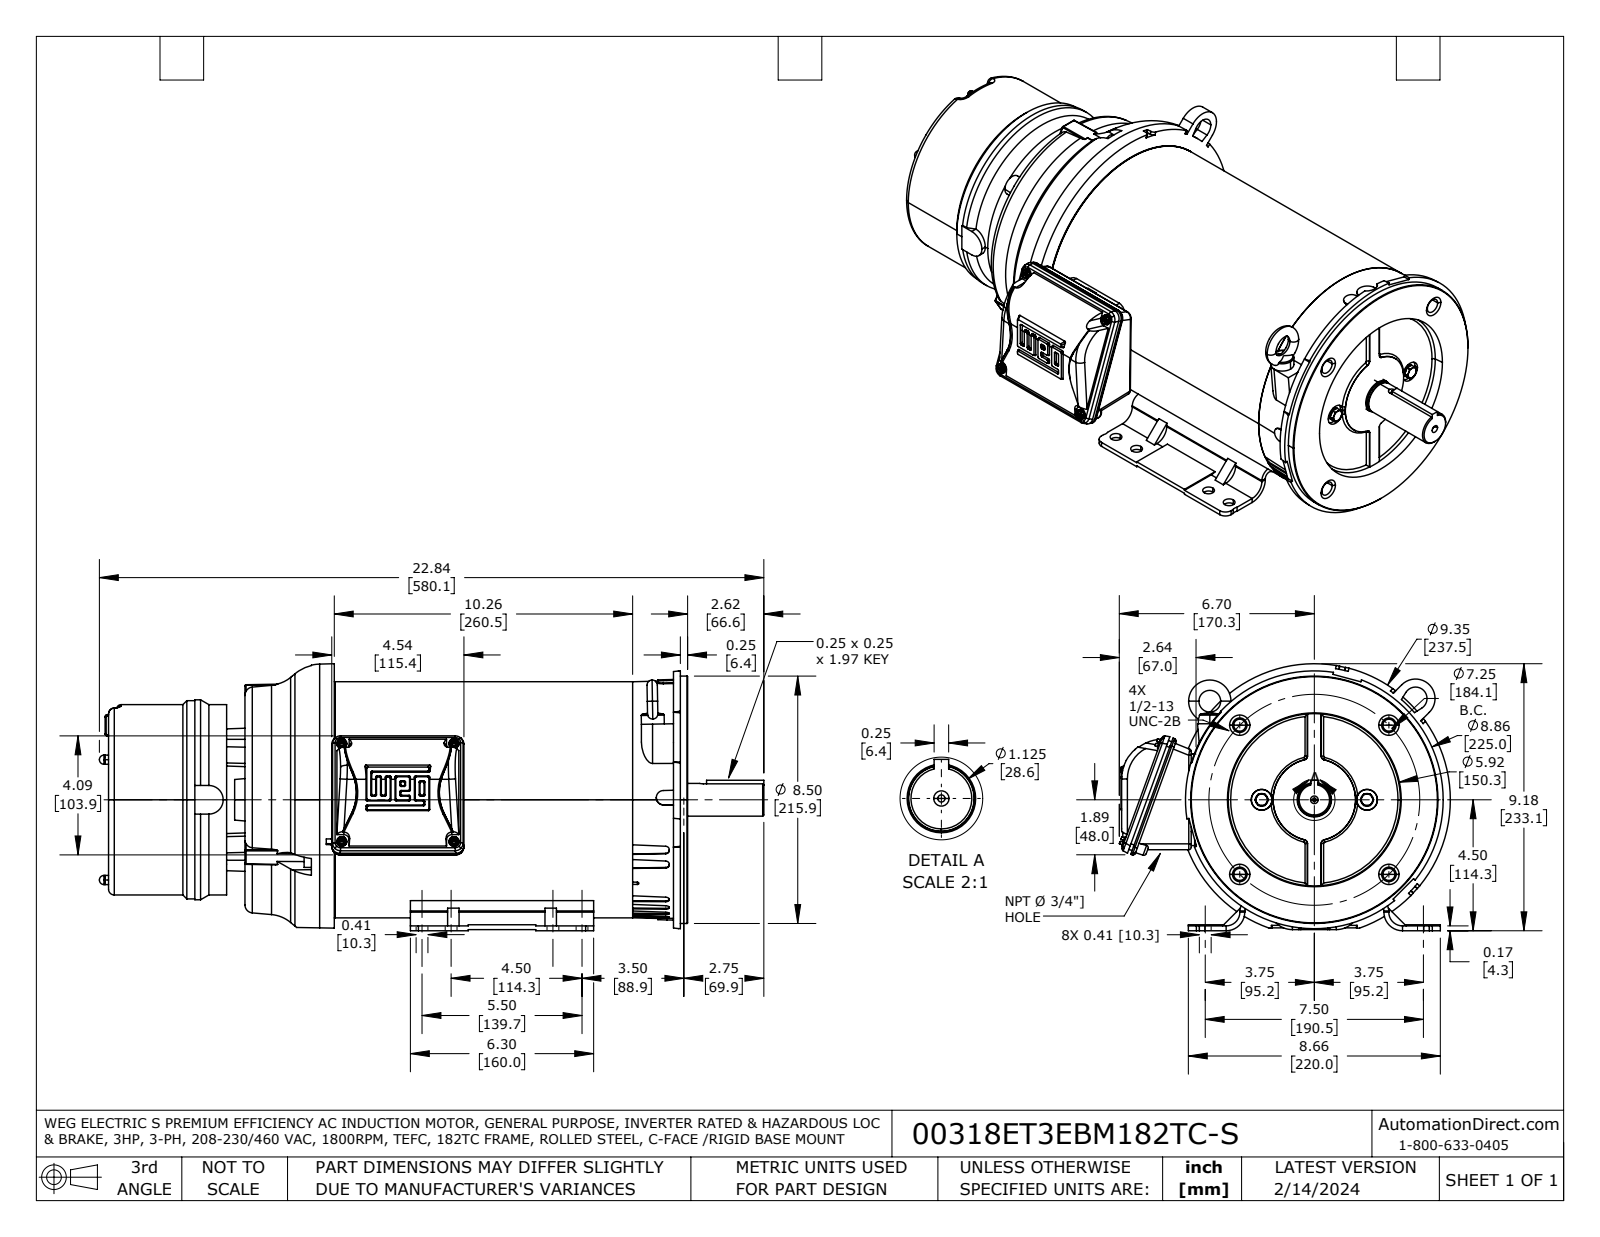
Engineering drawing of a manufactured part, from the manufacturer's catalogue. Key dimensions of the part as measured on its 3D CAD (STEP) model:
Part name (STEP PRODUCT): 00318ET3EBM182TC-S
STEP written by: SolidWorks 2021 (AUTOMOTIVE_DESIGN)
Units: inches
Bodies: 21 solids, 1366 faces (549 planar, 372 cylindrical, 445 other)
Overall size (bounding box): 22.841 × 11.38 × 9.175
Volume: 988.3 in³ · Surface area: 1 224 in²
Round holes (diameter × count): ⌀0.406 ×8, ⌀0.413 ×4, ⌀0.5 ×4, ⌀0.252 ×2, ⌀0.124 ×1
Round bosses / shafts (diameter × count): ⌀0.348 ×4, ⌀0.375 ×3, ⌀0.315 ×3, ⌀0.25 ×3, ⌀0.433 ×2, ⌀0.35 ×2, ⌀8.5 ×1, ⌀8.114 ×1
Partial cylindrical surfaces — rounded edges, fillets, slot ends (radius × count): R0.047 ×40, R0.126 ×22, R0.039 ×14, R0.087 ×12, R0.276 ×12, R0.079 ×10, R0.118 ×8, R0.205 ×8
Main face-to-face distances: 10.236, 3.72, 13.957, 0.167, 4.059, 7.78, 18.016, 19.906, 15.846, 12.126
Hole centre spacings: 1, 4.5, 5.07, 7.5, 7.567, 8.746, 1.811, 2.671
